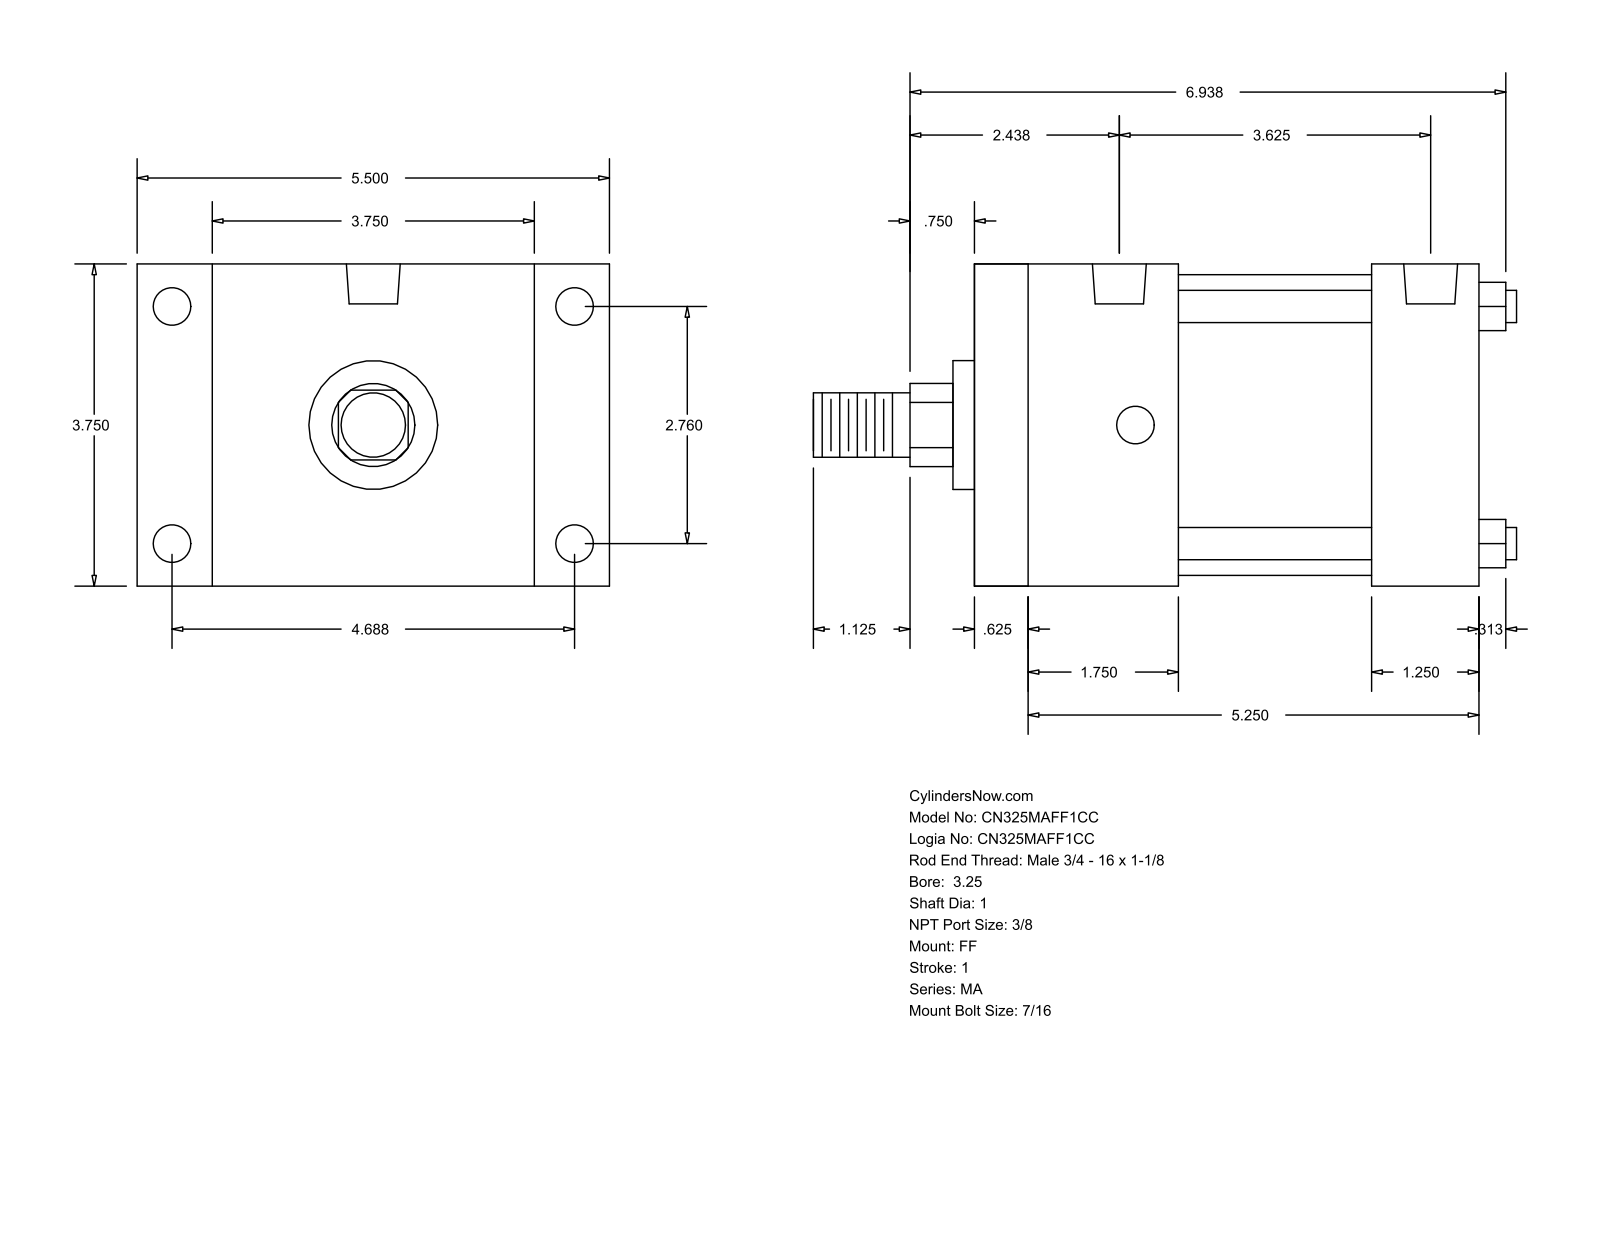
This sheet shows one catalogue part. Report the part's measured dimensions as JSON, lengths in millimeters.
{"part_name": "MA_FF__0325_1", "step_written_by": "GSSL Pune (CONFIG_CONTROL_DESIGN)", "units": "millimeters", "bodies": {"solids": 0, "faces": 92, "planar": 64, "cylindrical": 28, "other": 0}, "overall_size": [207.96, 139.7, 95.25], "round_holes": [[11.11, 8], [15.93, 2]], "round_bosses_or_shafts": [[9.53, 4], [88.9, 1], [38.1, 1], [25.4, 1], [19.05, 1]], "partial_cylinders_radius": [[12.29, 1]], "face_to_face_distances": [95.24, 149.23, 15.87, 133.36, 22.23, 117.47, 60.33, 117.48, 44.46, 101.61], "hole_center_spacings": [70.1, 82.55, 119.06, 138.16, 4.76, 4.77, 87.31, 87.32]}
